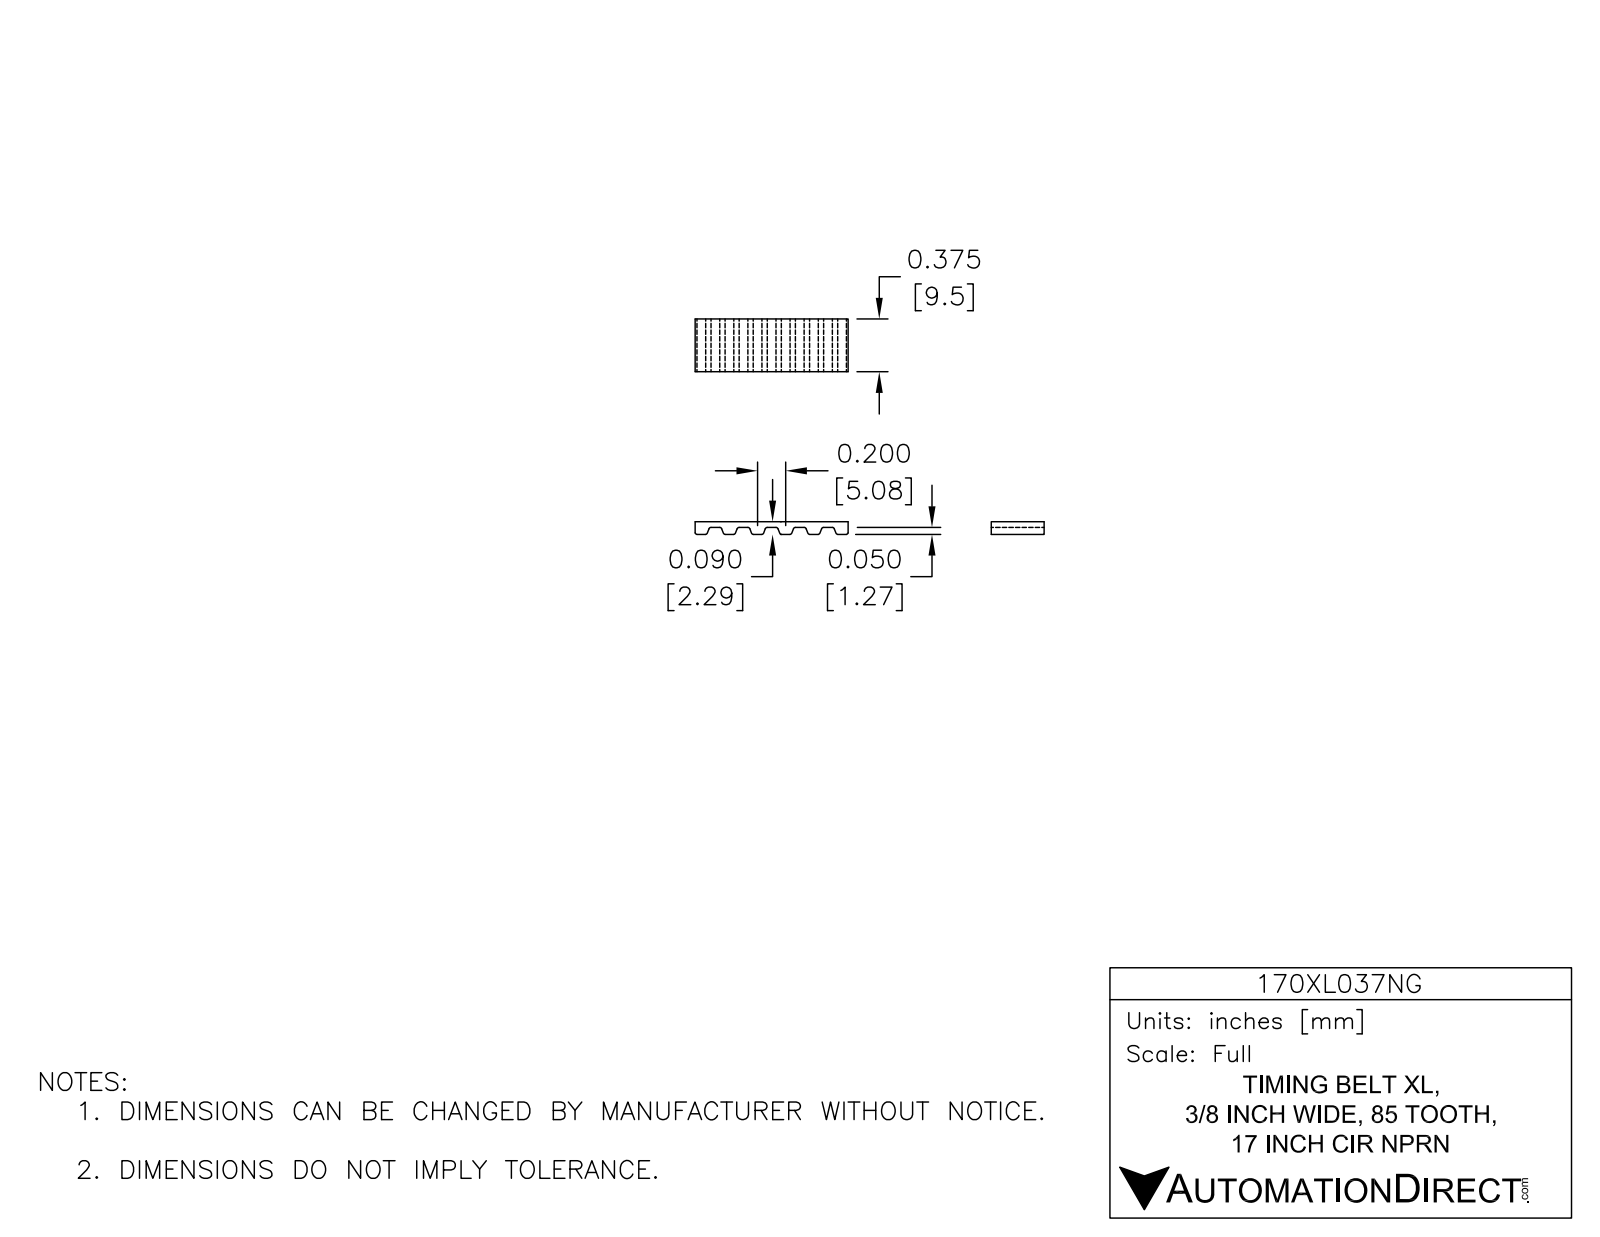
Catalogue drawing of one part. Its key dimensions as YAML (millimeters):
part_name: "170XL037NG"
step_written_by: "SolidWorks 2014 (AUTOMOTIVE_DESIGN)"
units: millimeters
bodies: {solids: 1, faces: 719, planar: 298, cylindrical: 421, other: 0}
overall_size: [172.4, 76.2, 9.5]
volume: 5670
surface_area: 10490
partial_cylinders:
  - {radius: 0.4, count: 340}
  - {radius: 37.1, count: 2}
  - {radius: 38.1, count: 2}
face_to_face_distances: [76.2, 1, 75.2, 9.5, 74.2, 9.1, 13.6, 18.1, 4.5, 22.7]
